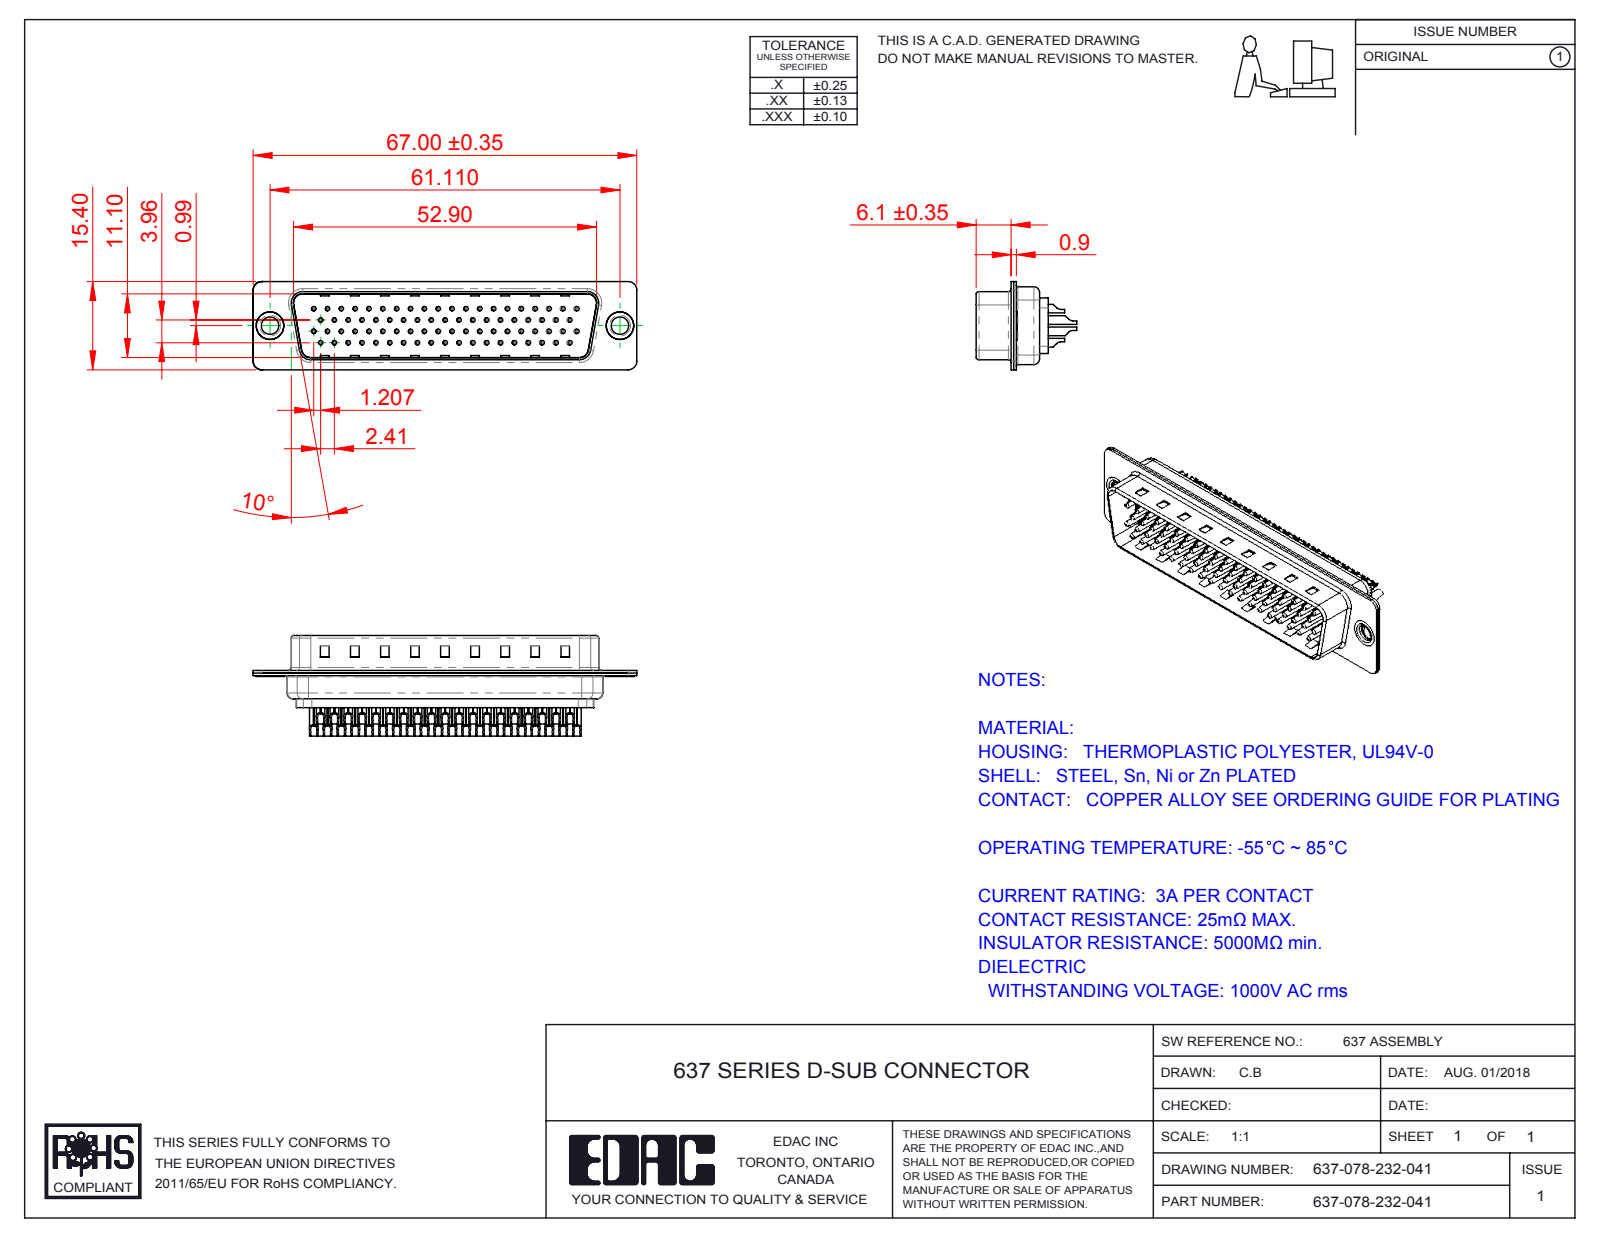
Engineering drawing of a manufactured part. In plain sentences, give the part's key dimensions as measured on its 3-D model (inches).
The part is named "637 Contact Row 3_32; 637 Shell Front_78 Contacts; 637 Shell Rear_78 Contacts; 637-078-232-041 (+5 more)". Its 3-D file was written by "SolidWorks 2016 (CONFIG_CONTROL_DESIGN)". It is 83 solids with 5378 faces: 1295 planar, 2387 cylindrical and 1696 other. Overall it measures 2.638 by 0.691 by 0.606 inches. Its volume is 0.266 cubic inches and its surface area 25.78 square inches. Round holes: 150 of diameter 0.063, 78 of diameter 0.014, 78 of diameter 0.043, 72 of diameter 0.03, 72 of diameter 0.079, 3 of diameter 0.157, 2 of diameter 0.12, 2 of diameter 0.189. Round bosses or shafts: 78 of diameter 0.079, 78 of diameter 0.059, 78 of diameter 0.03, 2 of diameter 0.197, 2 of diameter 0.193, 2 of diameter 0.14, 1 of diameter 0.189. Partial cylindrical surfaces (rounded edges, fillets, slot ends): 16 of radius 0.059, 12 of radius 0.079, 8 of radius 0.02, 8 of radius 0.039, 4 of radius 0.01, 4 of radius 0.022, 4 of radius 0.028, 4 of radius 0.037. The main face-to-face distances are 0.018, 0.016, 0.059, 0.077, 0.469, 0.453, 0.028, 0.437, 0.035, 0.031. The hole center spacings are 0.095, 0.285, 0.239, 0.38, 0.274, 0.333, 0.572, 0.665.
